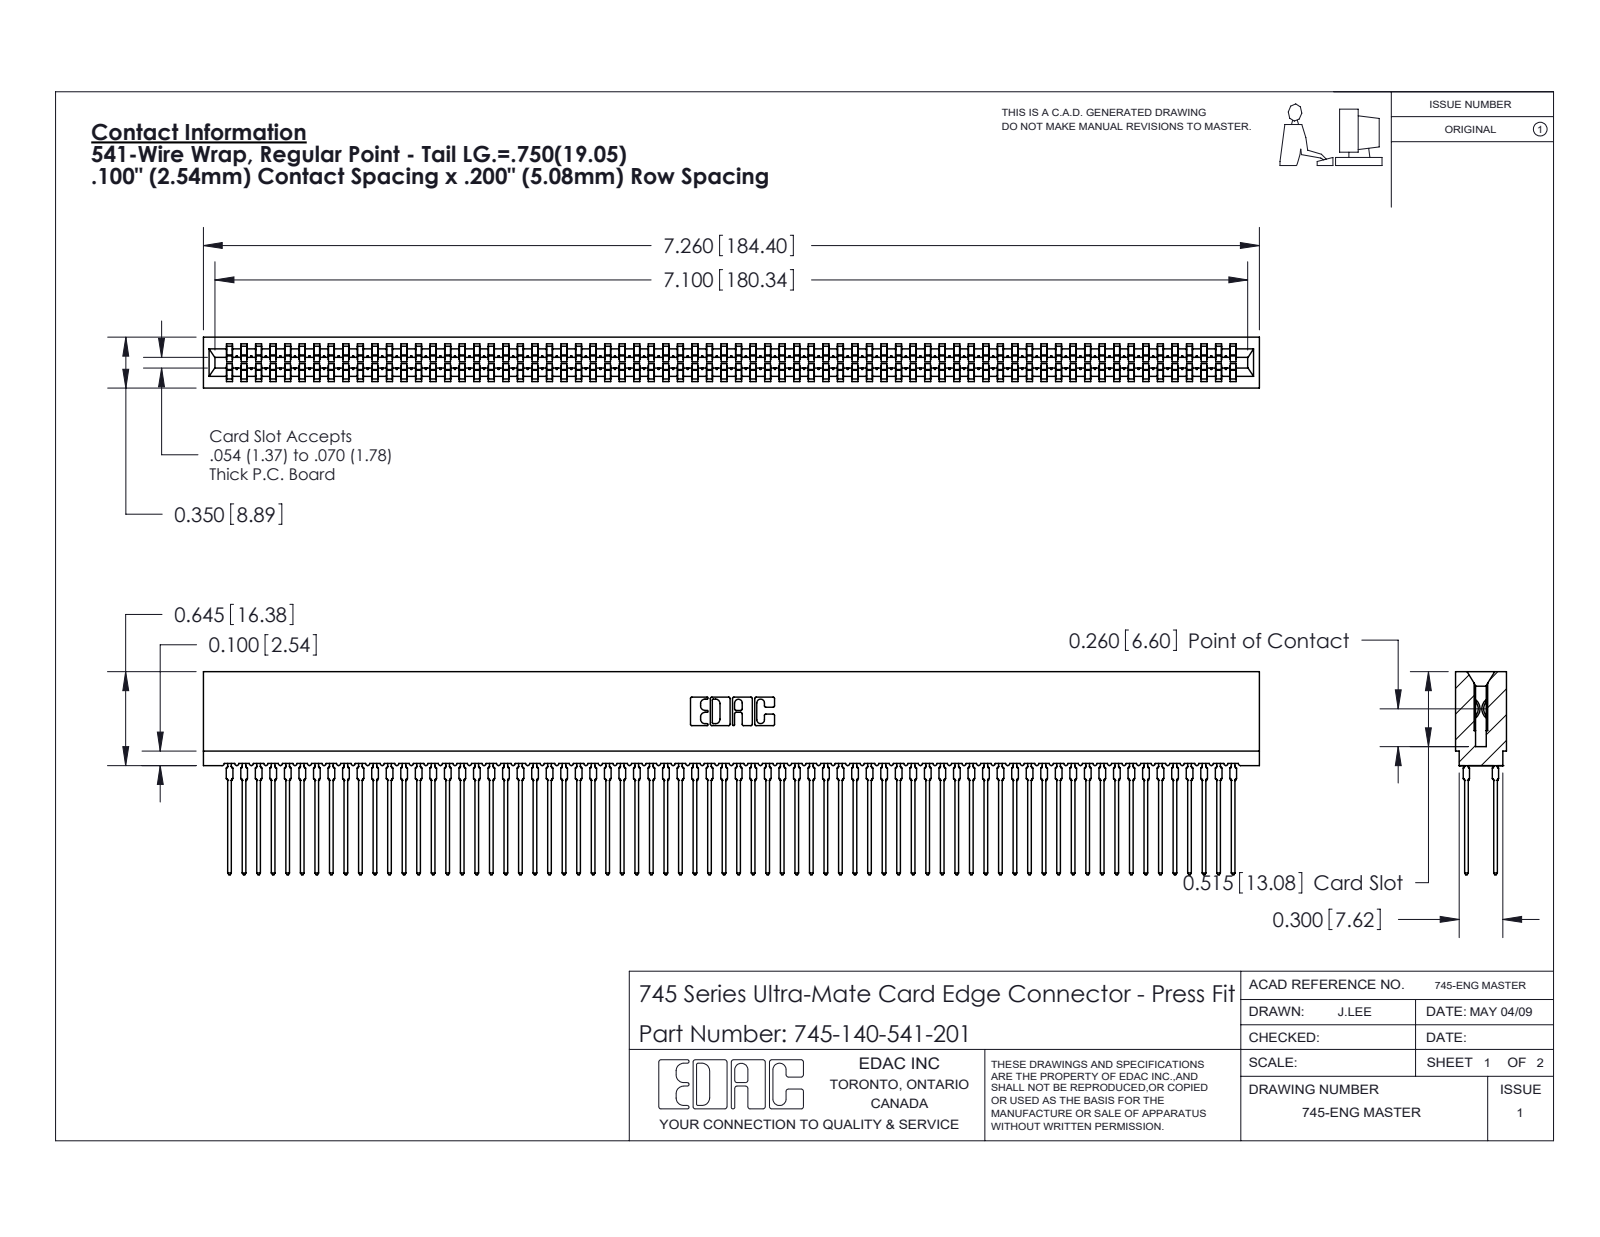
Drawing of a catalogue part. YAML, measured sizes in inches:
part_name: "745-292-001_541; 745-140-541-201; 745 Part_Insulator Option - 01"
step_written_by: "SolidWorks 2020 (CONFIG_CONTROL_DESIGN)"
units: inches
bodies: {solids: 141, faces: 12625, planar: 6495, cylindrical: 2490, other: 3640}
overall_size: [7.26, 1.396, 0.35]
volume: 1.045
surface_area: 59.27
partial_cylinders:
  - {radius: 0.021, count: 280}
  - {radius: 0.015, count: 140}
  - {radius: 0.01, count: 22}
  - {radius: 0.005, count: 8}
  - {radius: 0.011, count: 8}
  - {radius: 0.007, count: 6}
  - {radius: 0.031, count: 6}
  - {radius: 0.026, count: 3}
face_to_face_distances: [0.063, 0.287, 0.2, 0.35, 0.087, 0.263, 0.025, 0.045, 0.305, 0.018]
